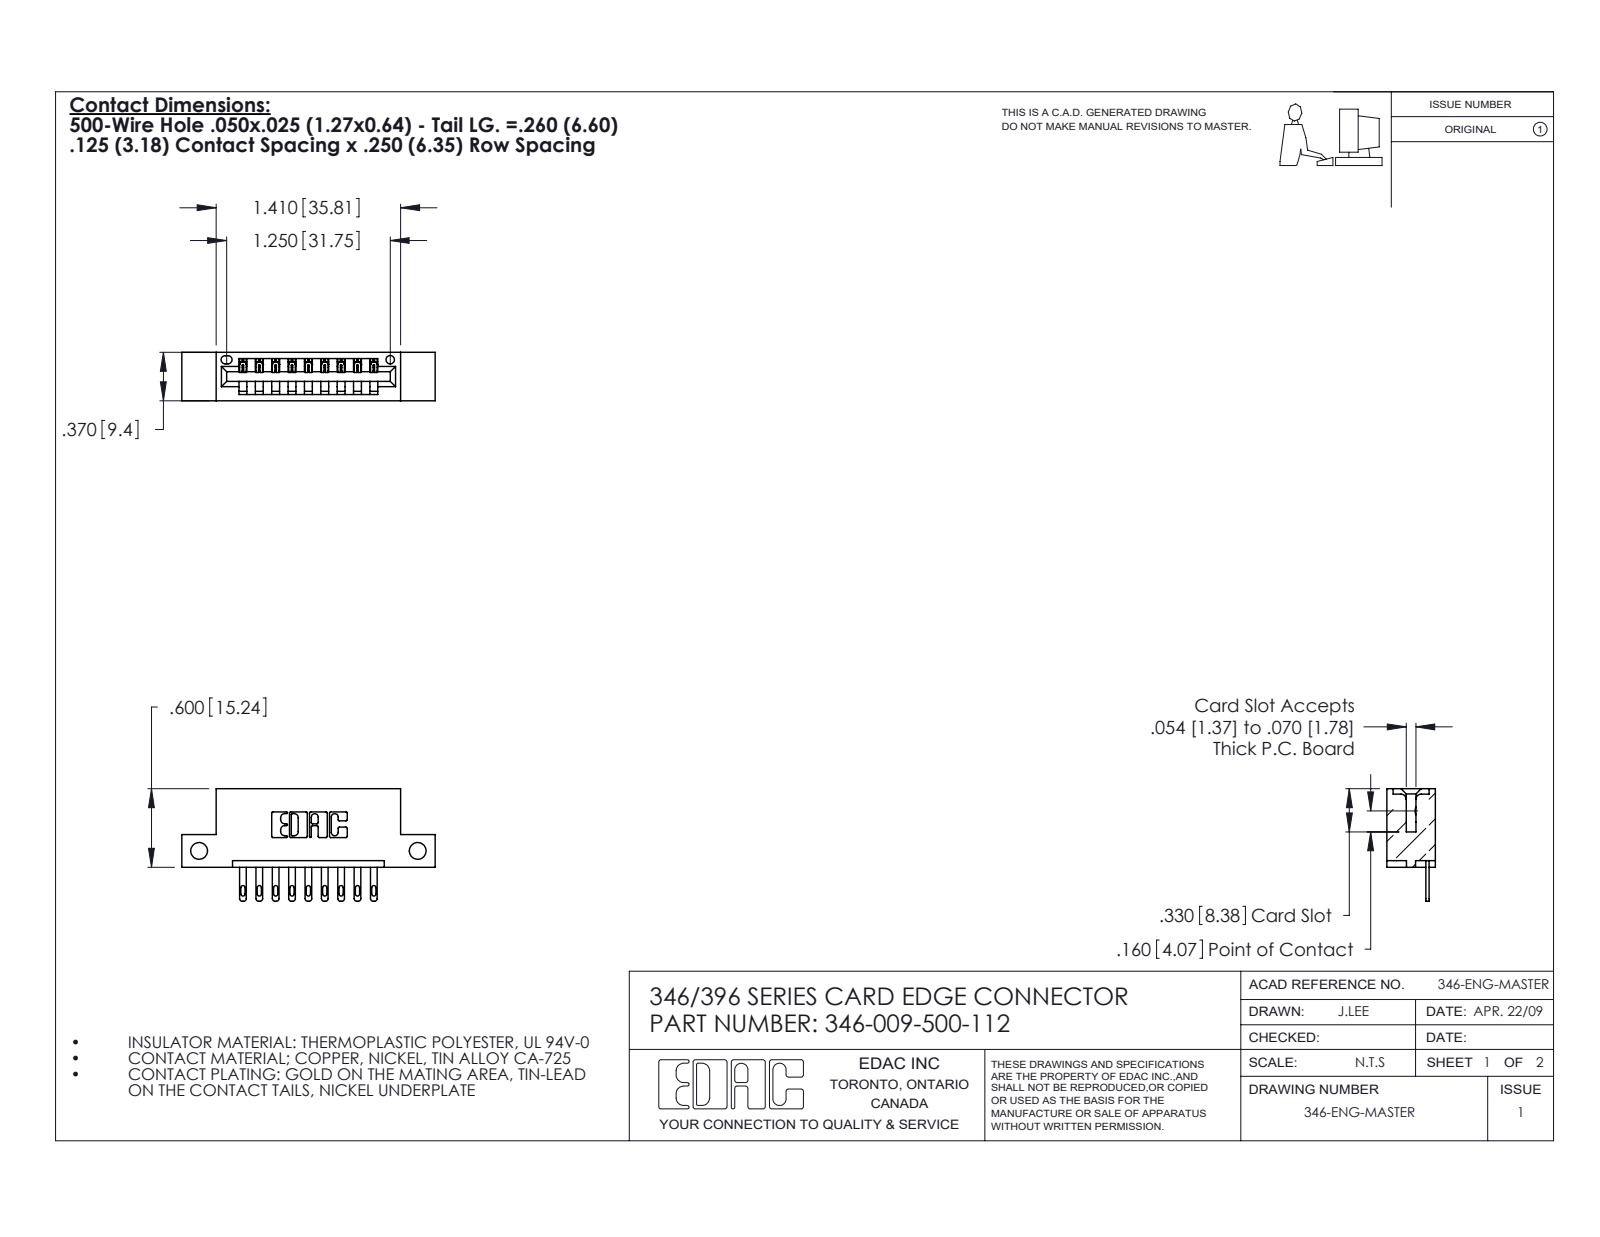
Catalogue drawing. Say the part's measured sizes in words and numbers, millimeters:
The part is named "345-292-001_345-293-100; 346-009-500-112; 346 Part_Flush Mounting Lugs - Side Mount". Its 3-D file was written by "SolidWorks 2020 (CONFIG_CONTROL_DESIGN)". It is 10 solids with 608 faces: 382 planar, 226 cylindrical and 0 other. Overall it measures 49.1 by 21.8 by 9.4 millimeters. Its volume is 4 390 cubic millimeters and its surface area 5 013 square millimeters. Round holes: 2 of diameter 3.3, 1 of diameter 1.6. Partial cylindrical surfaces (rounded edges, fillets, slot ends): 22 of radius 0.3, 18 of radius 0.2, 18 of radius 0.4, 18 of radius 0.5, 6 of radius 0.2, 6 of radius 0.8, 3 of radius 0.7, 2 of radius 0.8. The main face-to-face distances are 6.4, 1.2, 8.2, 9.4, 1.8, 7.6, 0.6, 3.8, 5.6, 2.5. The hole center spacings are 42.4.
